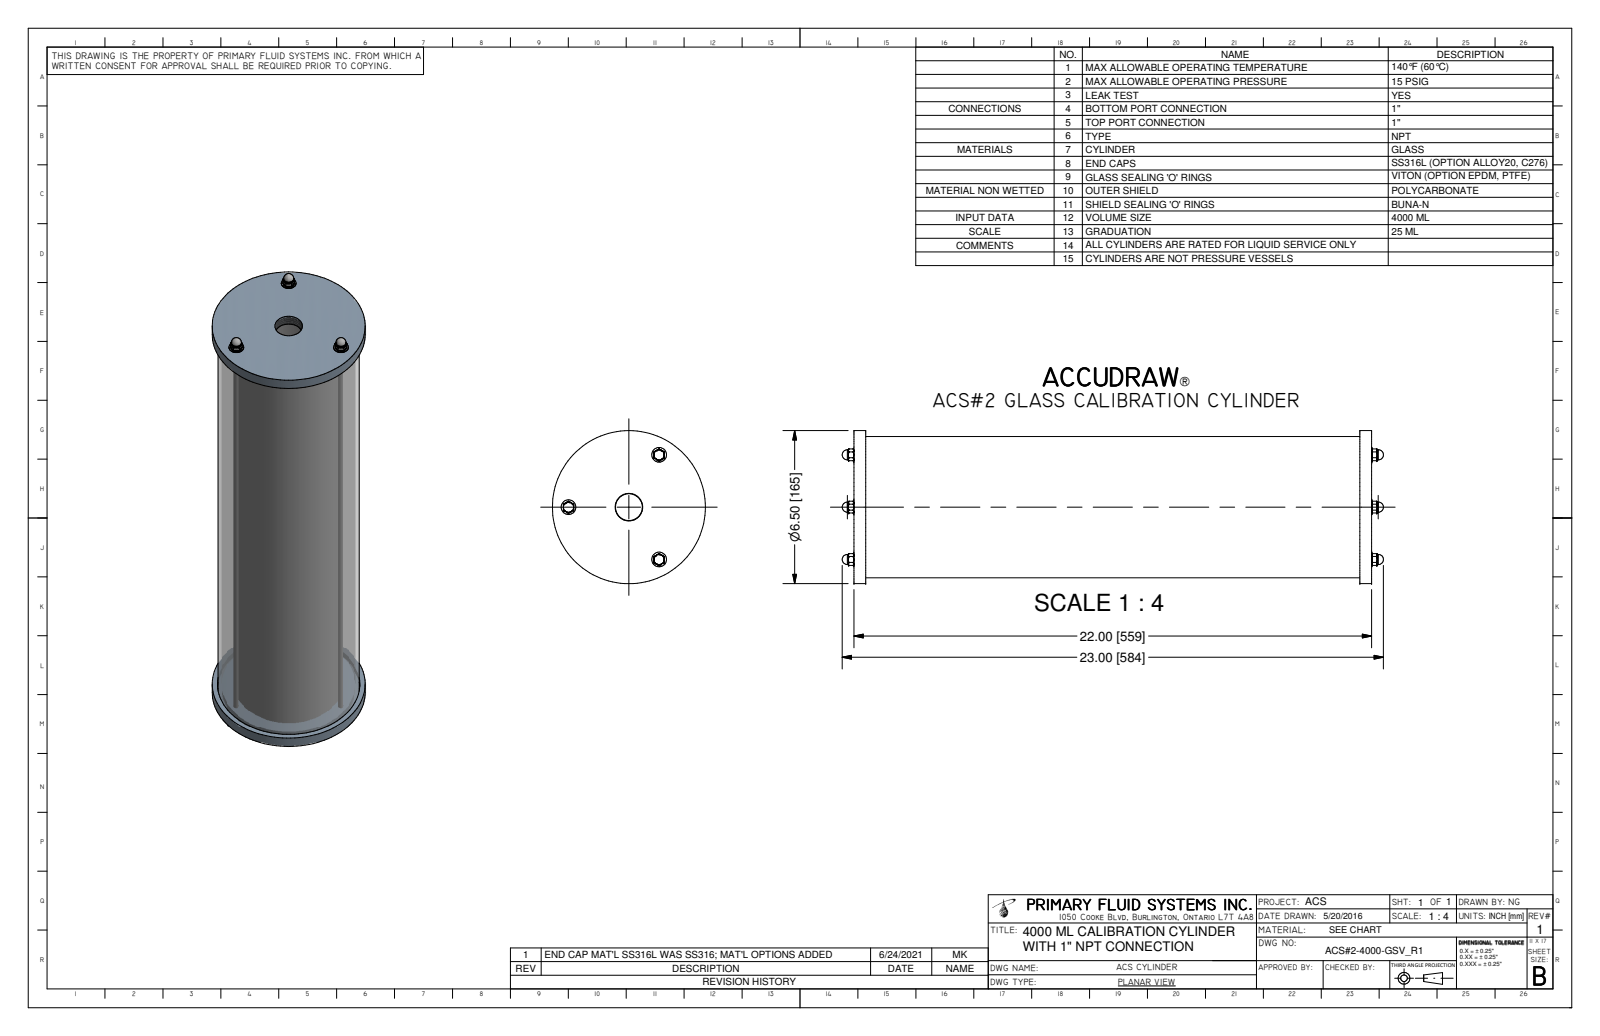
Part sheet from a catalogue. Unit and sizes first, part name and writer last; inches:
Units: inches
Overall size (bounding box): 23 × 6.5 × 6.5
Round holes (diameter × count): ⌀0.18 ×3, ⌀0.266 ×3, ⌀0.281 ×3, ⌀4.134 ×1, ⌀4.625 ×1, ⌀5.75 ×1, ⌀6.05 ×1
Round bosses / shafts (diameter × count): ⌀0.625 ×3, ⌀0.25 ×3, ⌀6.5 ×1, ⌀6 ×1, ⌀5.7 ×1, ⌀4.528 ×1, ⌀4 ×1
Main face-to-face distances: 22, 21.5, 0.5, 21, 0.25, 0.125, 21.875, 0.375, 21.375, 0.225
Hole centre spacings: 2.567, 4.446, 4.446
Volume: 137.4 in³ · Surface area: 1 646 in²
Bodies: 19 solids, 425 faces (38 planar, 41 cylindrical, 346 other)
Part name (STEP PRODUCT): ACS#2-4000-GSV_R0; ACS-3-4000-METAL_R3; ACS-2-4000-PC_R6; ACS-1-4000-A_R0 (+3 more)
STEP written by: Autodesk Inventor 2009 (AUTOMOTIVE_DESIGN)
